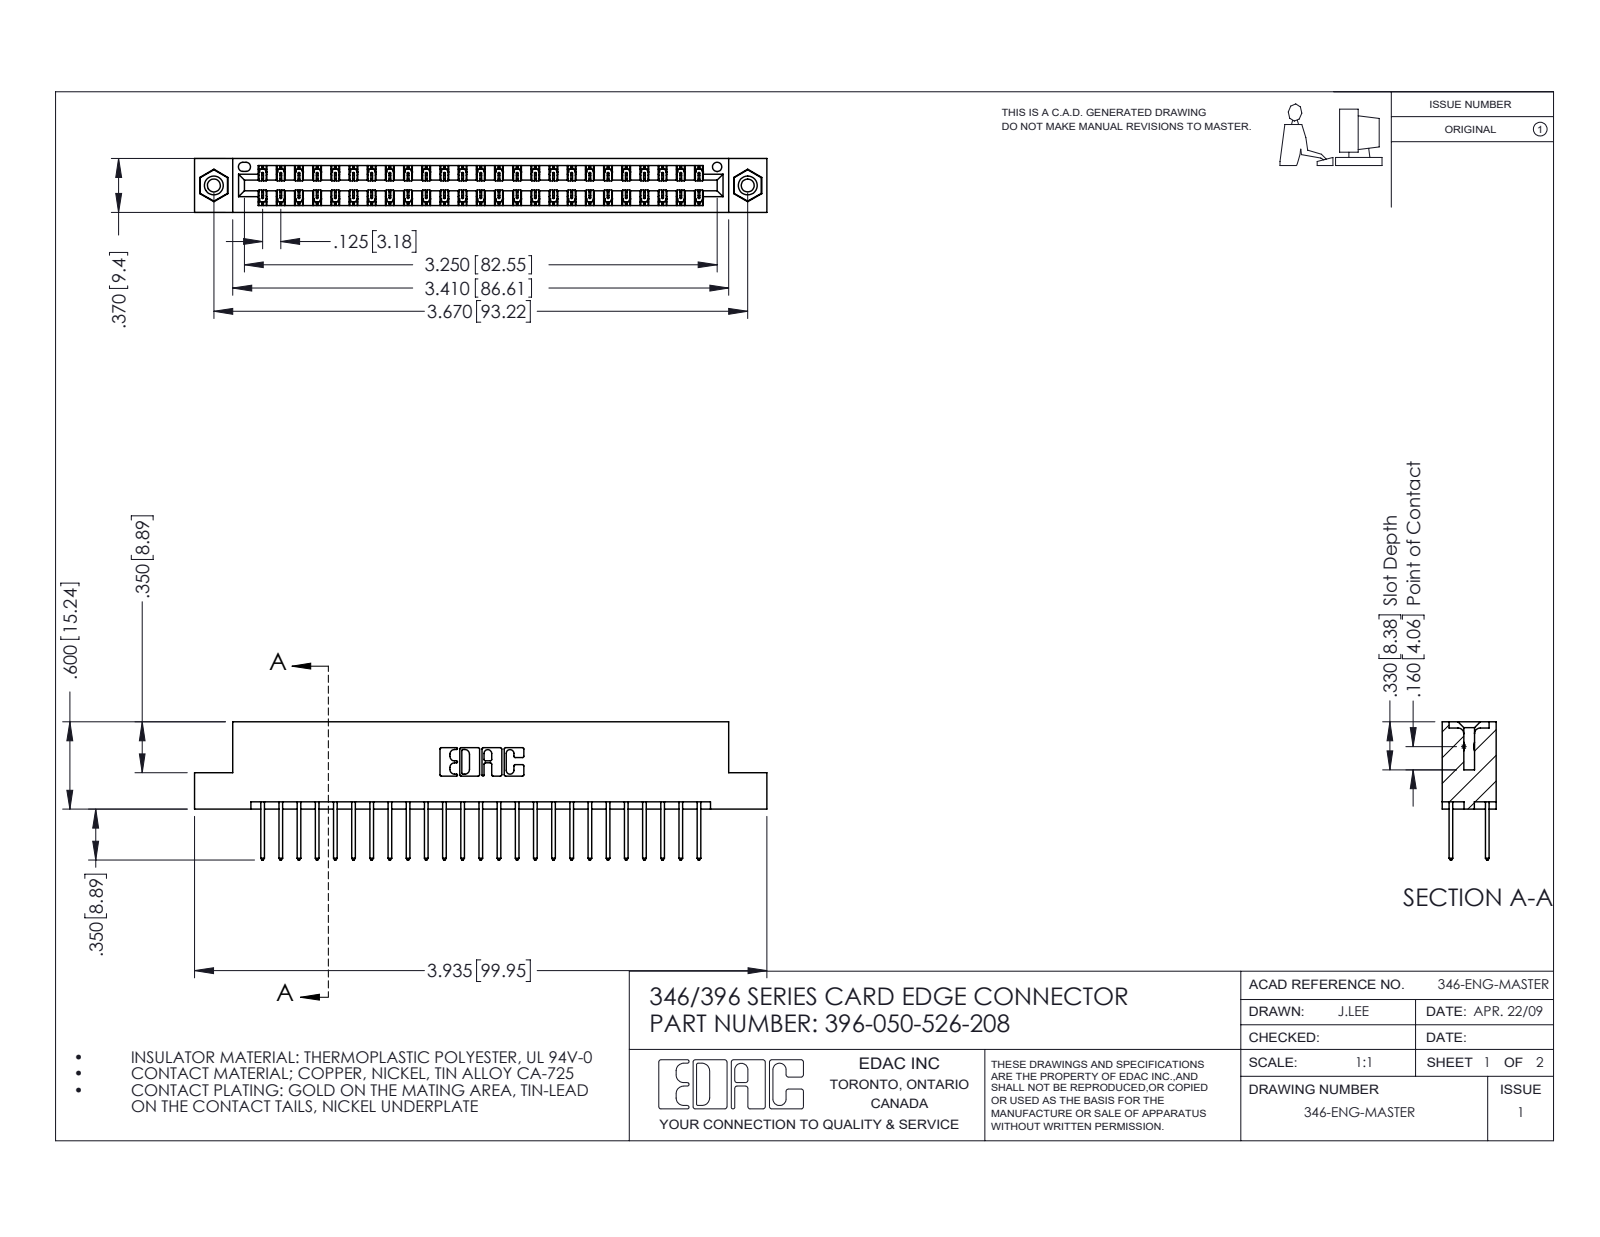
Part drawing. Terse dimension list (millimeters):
name: 345-250-001_345-250-003-102; 396-050-526-208; 345-292-001_345-293-126; 346 Part_Flush Mounting Lugs - 0.156 Dia-TI
written by: SolidWorks 2016 (CONFIG_CONTROL_DESIGN)
unit: mm
bodies: 53 solids, 2782 faces (1858 planar, 908 cylindrical, 16 other)
size: 99.9 × 24.1 × 9.4
volume: 9 680 mm³; area: 13 440 mm²
holes: 2× ⌀2.3, 2× ⌀3.2, 2× ⌀4, 1× ⌀1.6
bosses: 2× ⌀3.9
rounds: 75× R0.2, 50× R0.3, 22× R0.3, 6× R0.2, 6× R0.8, 3× R0.7, 2× R0.4, 2× R0.6
face distances: 1.2, 8.2, 6.4, 9.4, 1.8, 7.6, 0.6, 7, 3.8, 5.6
hole spacings: 6.2, 87.9, 93.2
